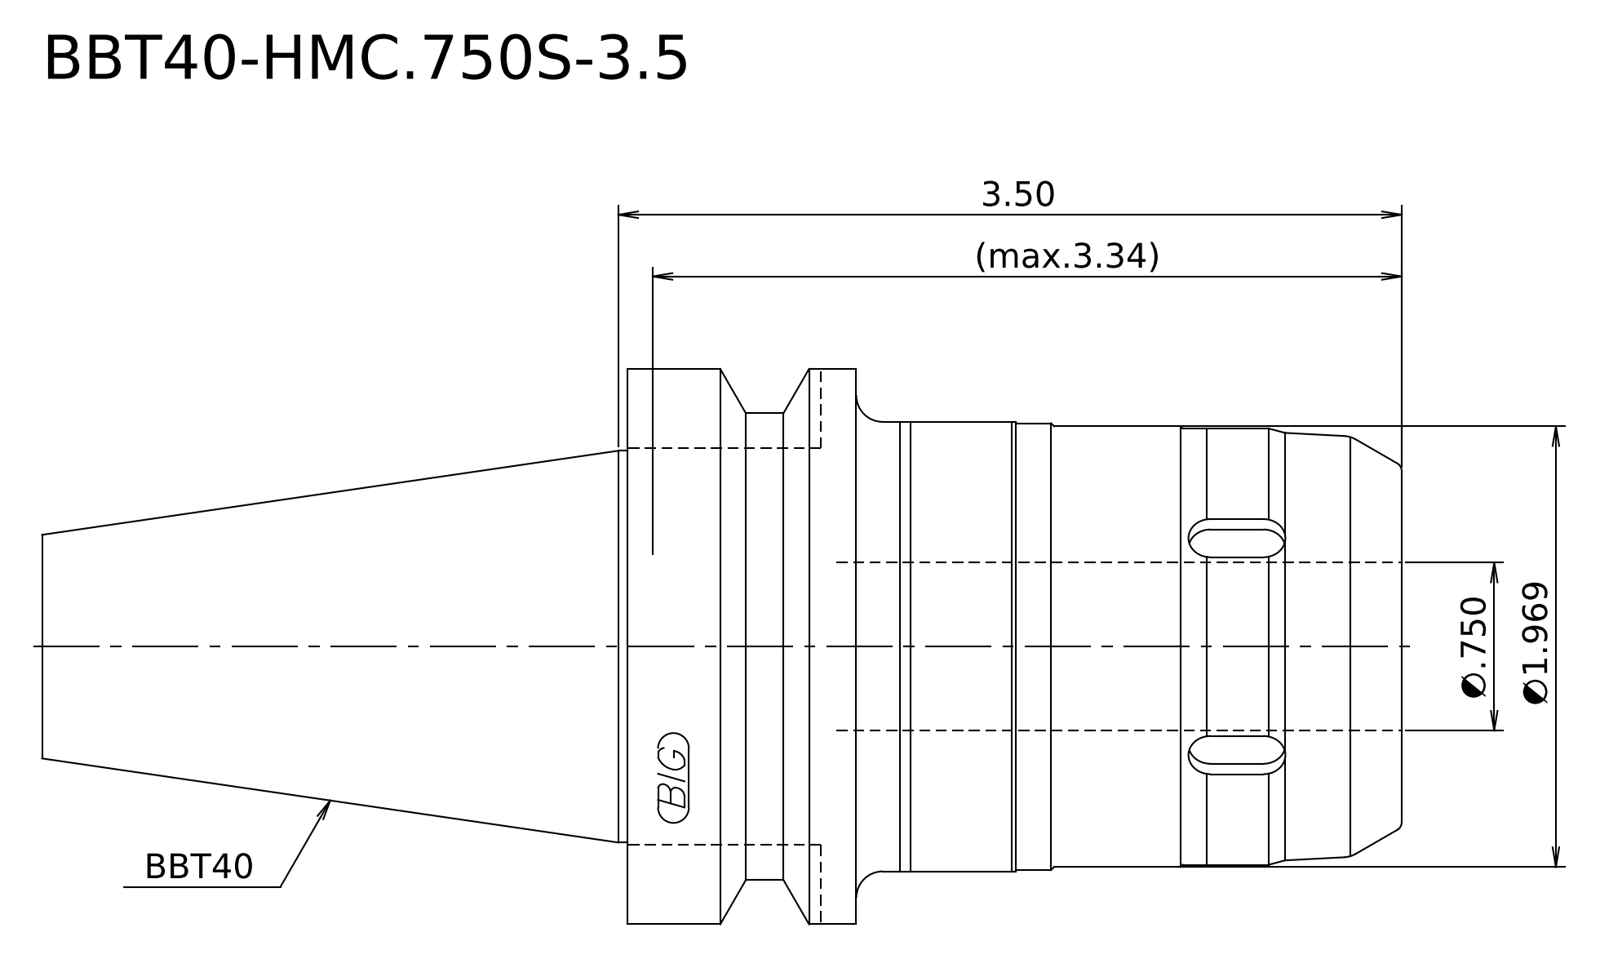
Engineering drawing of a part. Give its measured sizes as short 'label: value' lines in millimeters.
written by: Kubotek KeyCreator 2011 V10.0.2 (22737) (automotive_design)
unit: mm
bodies: 1 solid, 22 faces (5 planar, 8 cylindrical, 9 other)
size: 154.3 × 63 × 63
volume: 260 078 mm³; area: 27 378 mm²
bosses: 1× ⌀63, 1× ⌀53, 1× ⌀51, 1× ⌀50.7, 1× ⌀50, 1× ⌀49.5, 1× ⌀44.45
face distances: 87.9, 61.9, 26, 154.3, 92.4, 66.4, 43.8, 18.1, 44.1, 110.5
